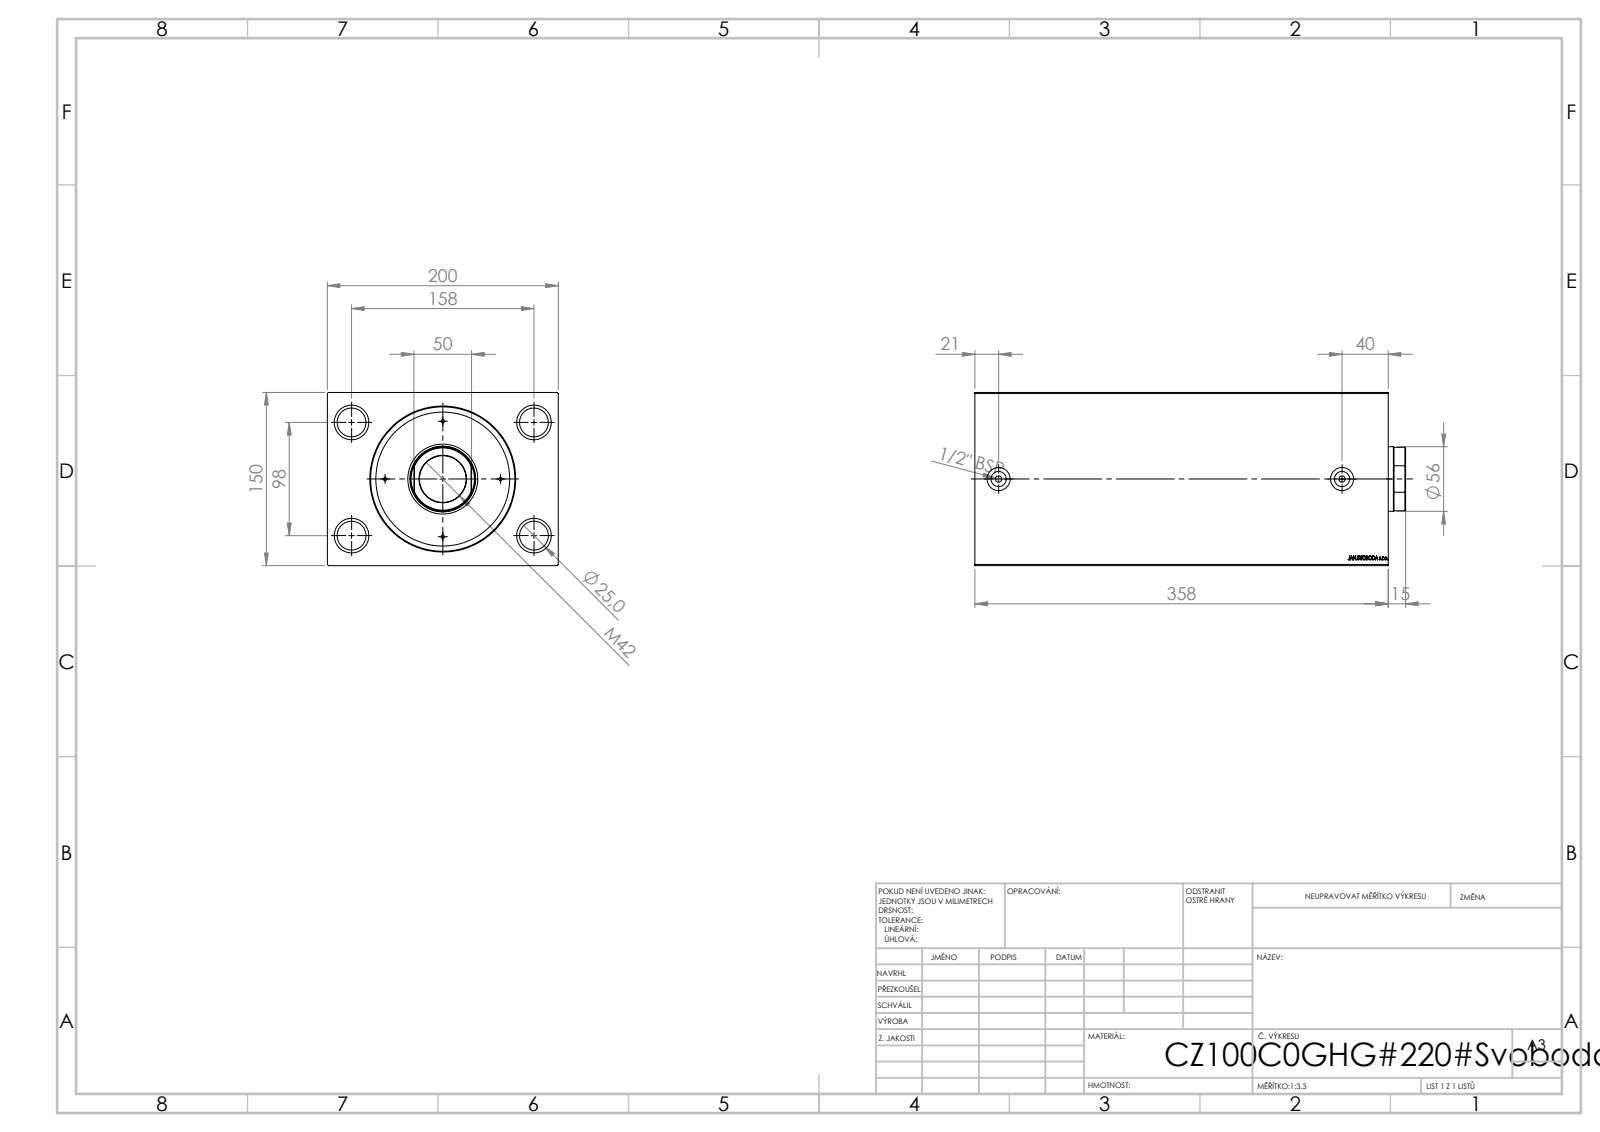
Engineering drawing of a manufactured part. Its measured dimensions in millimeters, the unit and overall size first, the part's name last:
Units: millimetres
Overall size (bounding box): 358 × 200 × 150
Round holes (diameter × count): ⌀25 ×4, ⌀30 ×4, ⌀5.5 ×2, ⌀8 ×2, ⌀13.16 ×2, ⌀20 ×2, ⌀36 ×1, ⌀100 ×1, ⌀125 ×1
Main face-to-face distances: 150, 200, 358, 324.7, 33.3, 15, 309.7, 343, 10.33, 347.67
Hole centre spacings: 92.96, 98, 158, 185.92, 277.5, 297.5
Volume: 7 398 000 mm³ · Surface area: 524 216 mm²
Bodies: 1 solid, 825 faces (397 planar, 46 cylindrical, 382 other)
STEP written by: SolidWorks 2019 (CONFIG_CONTROL_DESIGN)
